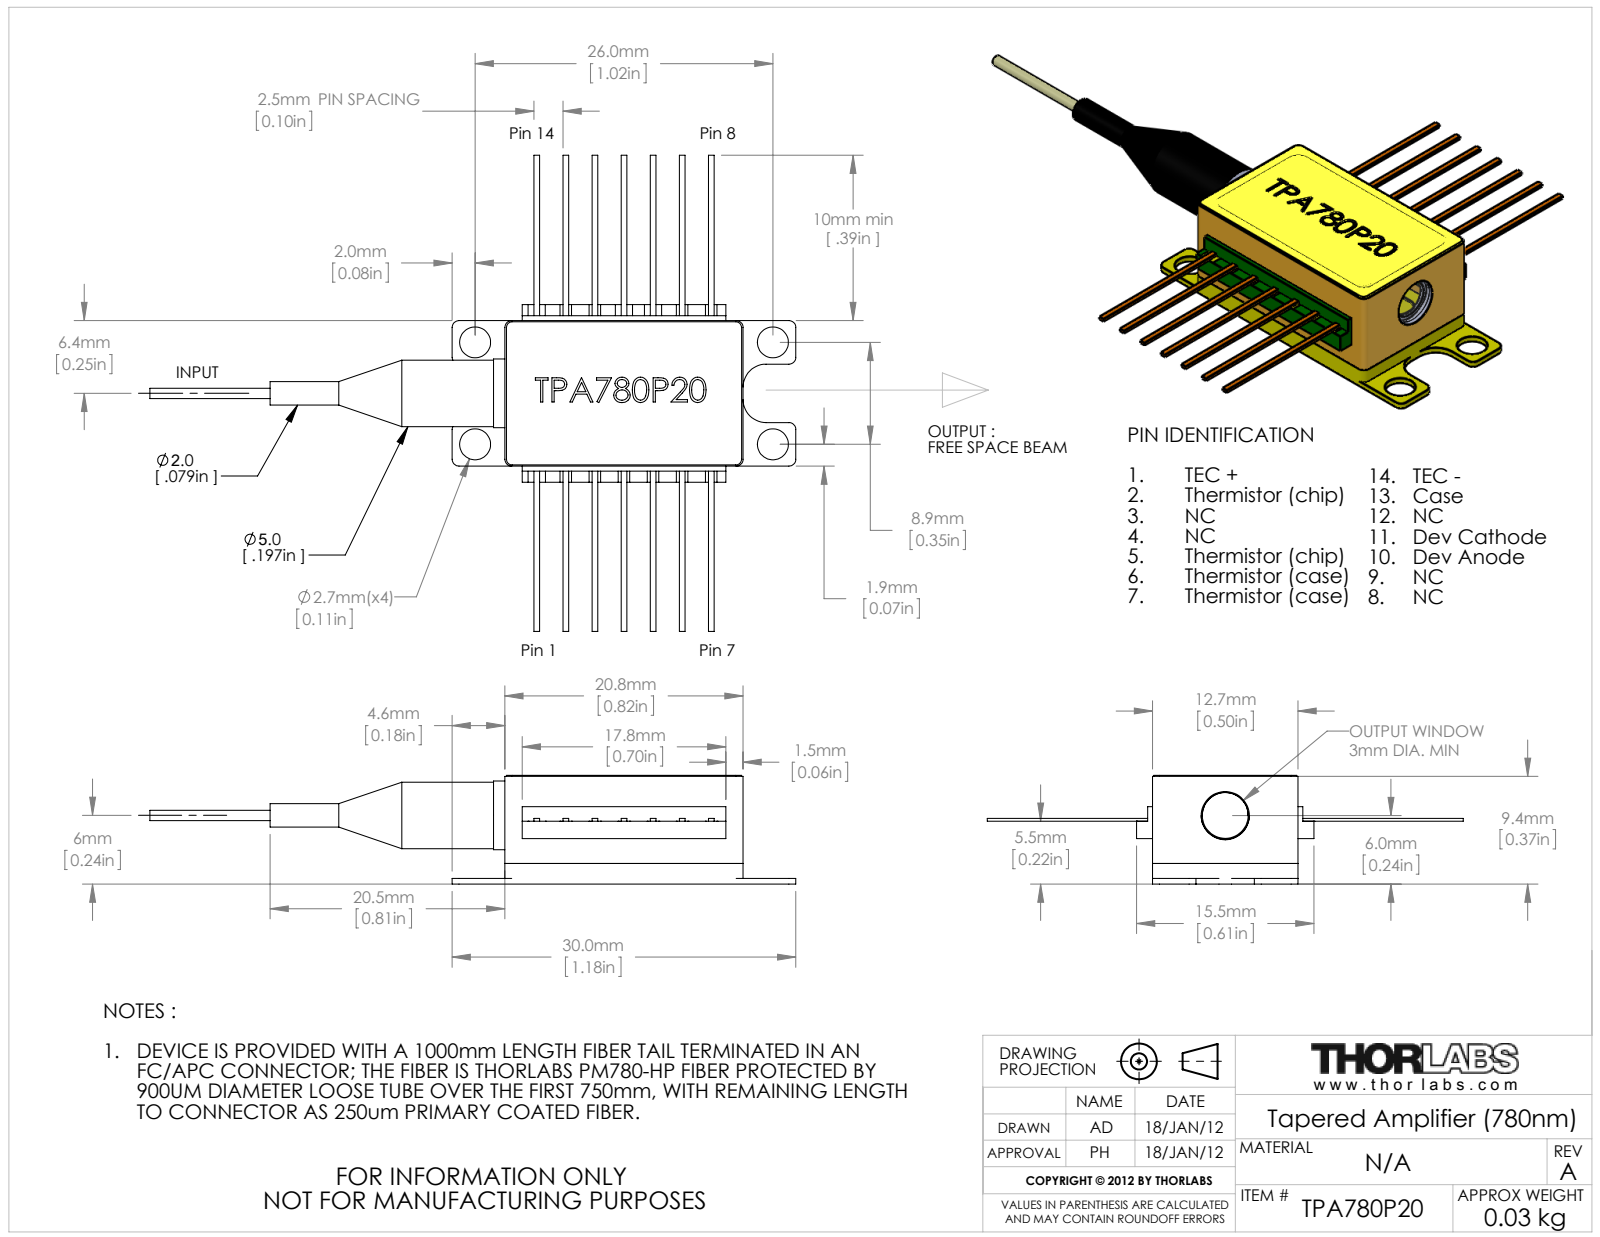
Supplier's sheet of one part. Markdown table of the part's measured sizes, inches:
| quantity | value |
| --- | --- |
| part name | 22606-E0W; 32025-000 Lid (Labelled for TPA780P20); TPA 14pin butterfly package |
| STEP written by | SolidWorks 2011 (AUTOMOTIVE_DESIGN) |
| units | inches |
| bodies | 1 solid, 407 faces (278 planar, 70 cylindrical, 59 other) |
| overall size | 2.22 × 1.636 × 0.374 |
| volume | 0.004 in³ |
| surface area | 5.194 in² |
| round holes (diameter × count) | 0.106 × 4, 0.043 × 1, 0.082 × 1, 0.134 × 1, 0.165 × 1 |
| round bosses / shafts (diameter × count) | 0.236 × 1, 0.228 × 1, 0.157 × 1, 0.08 × 1, 0.079 × 1, 0.035 × 1 |
| partial cylindrical surfaces (radius × count) | 0.024 × 12, 0.039 × 12, 0.008 × 4, 0.02 × 4, 0.079 × 4, 0.005 × 2 |
| main face-to-face distances | 0.039, 0.374, 0.299, 0.362, 0.461, 0.5, 0.071, 0.291, 0.303, 0.37 |
| hole center spacings | 0.35, 1.024, 1.082 |
